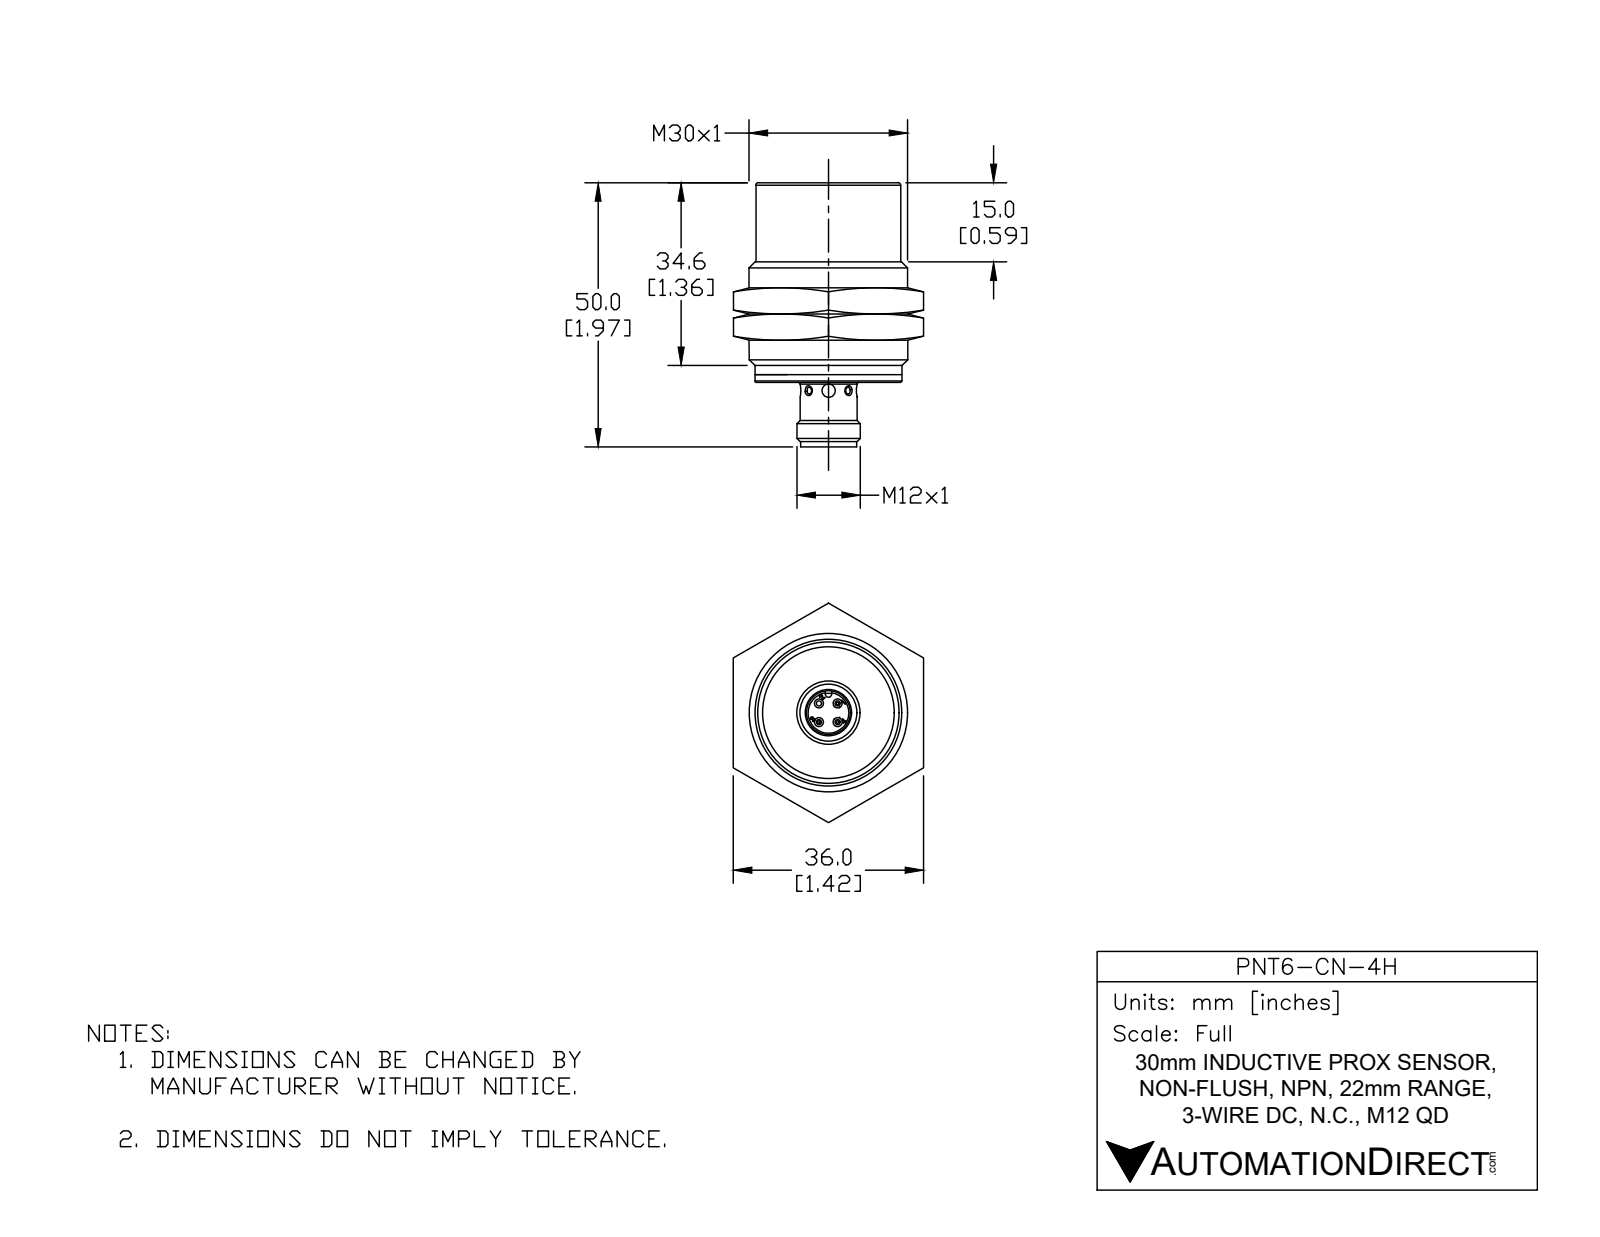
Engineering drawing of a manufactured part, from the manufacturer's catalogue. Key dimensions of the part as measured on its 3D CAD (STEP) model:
Part name (STEP PRODUCT): PNT6-CN-4H
STEP written by: SolidWorks 2017 (AUTOMOTIVE_DESIGN)
Units: inches
Bodies: 1 solid, 515 faces (161 planar, 130 cylindrical, 224 other)
Overall size (bounding box): 1.969 × 1.181 × 1.181
Volume: 1.573 in³ · Surface area: 12.79 in²
Round holes (diameter × count): ⌀0.043 ×3, ⌀0.04 ×2, ⌀0.098 ×2, ⌀0.038 ×1, ⌀0.04 ×1, ⌀0.323 ×1, ⌀0.327 ×1, ⌀0.394 ×1, ⌀1.047 ×1, ⌀1.076 ×1, ⌀1.089 ×1
Round bosses / shafts (diameter × count): ⌀0.039 ×9, ⌀1.181 ×1, ⌀1.094 ×1, ⌀1.083 ×1, ⌀1.074 ×1, ⌀1.044 ×1, ⌀0.878 ×1, ⌀0.472 ×1
Partial cylindrical surfaces — rounded edges, fillets, slot ends (radius × count): R0.004 ×12, R0.02 ×8, R0.03 ×3, R0.039 ×3, R0.024 ×1, R0.031 ×1
Main face-to-face distances: 0.126, 1.488, 1.362, 0.037, 0.089, 1.451, 0.098, 1.461, 0.028, 0.024
Hole centre spacings: 0.098, 0.139, 0.197
